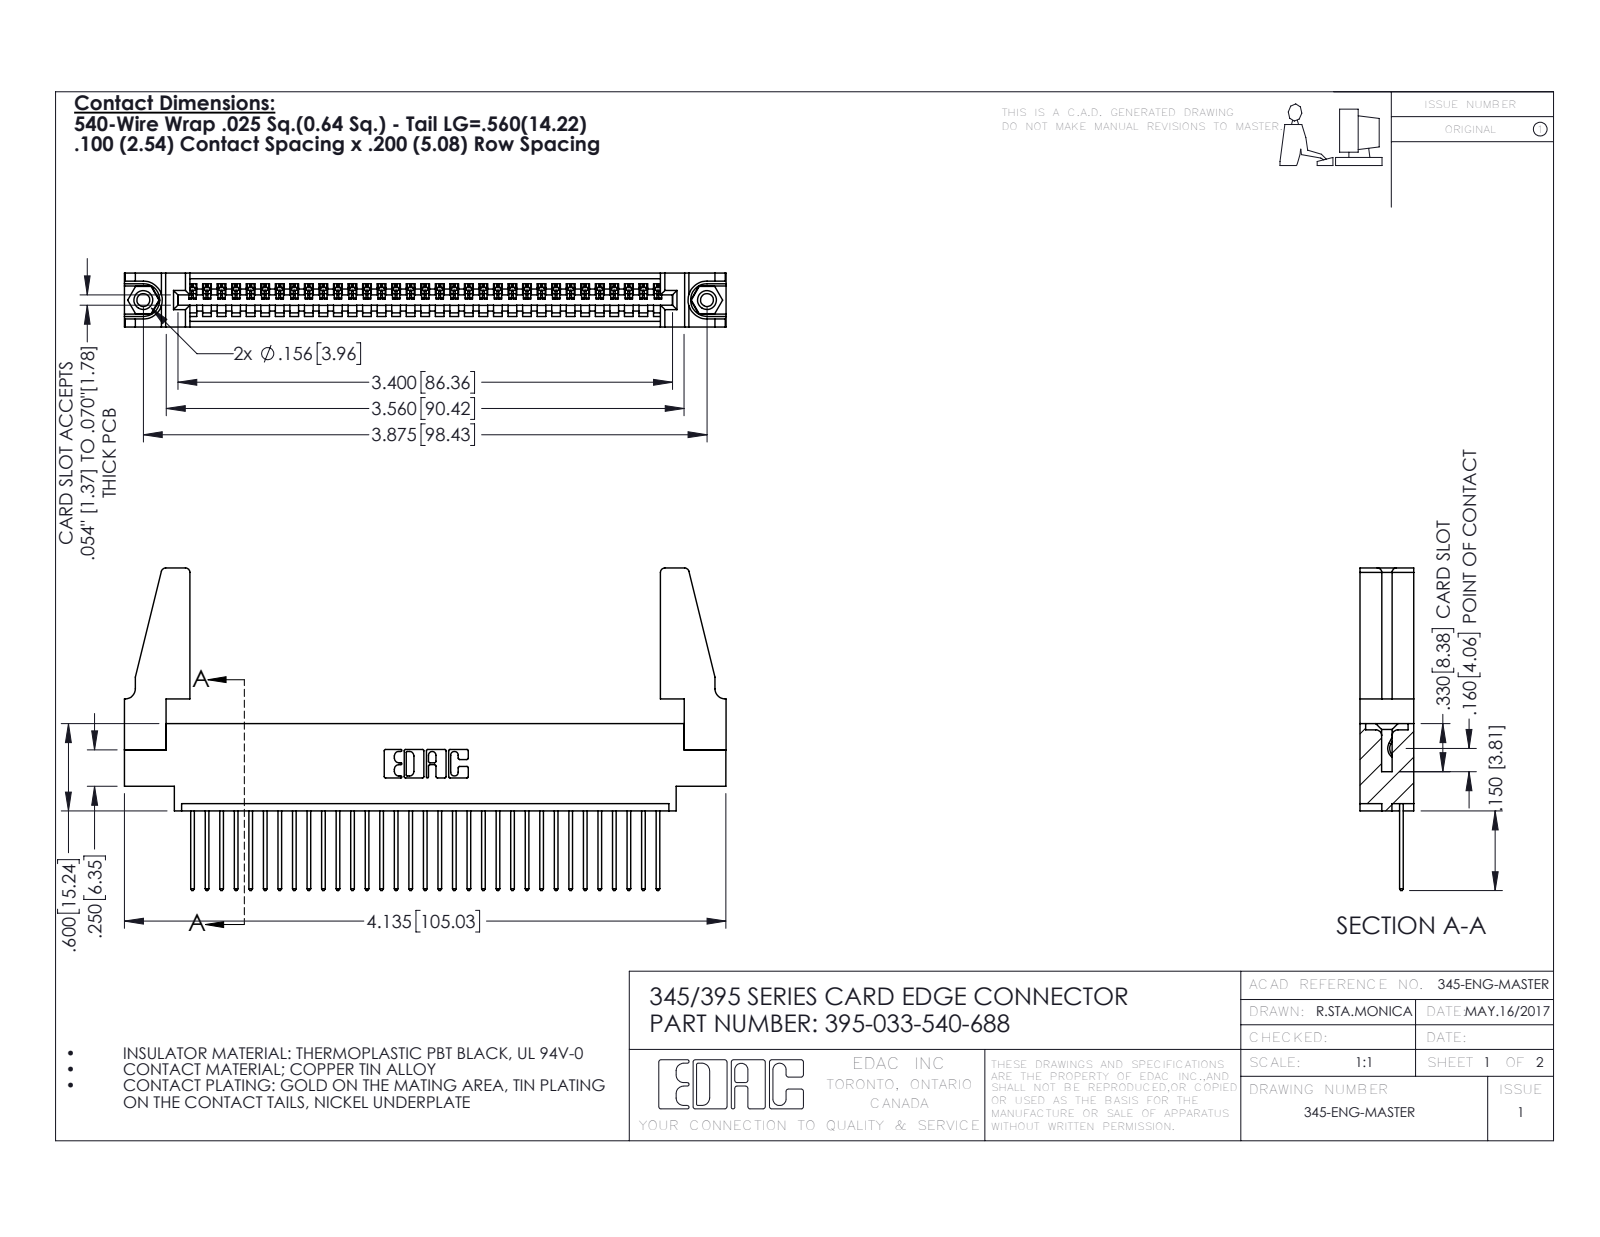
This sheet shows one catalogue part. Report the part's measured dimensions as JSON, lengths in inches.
{"part_name": "345-292-001_345-293-140; 345-220-078_345-220-088; 395-033-540-688; 345 Part_0.170 Offset - 0.156 Dia-TH (+1 more)", "step_written_by": "SolidWorks 2016 (CONFIG_CONTROL_DESIGN)", "units": "inches", "bodies": {"solids": 38, "faces": 2168, "planar": 1476, "cylindrical": 676, "other": 16}, "overall_size": [4.136, 2.217, 0.37], "volume_in3": 0.799, "surface_area_in2": 25.62, "round_holes": [[0.089, 2], [0.125, 2], [0.156, 2], [0.064, 1]], "round_bosses_or_shafts": [[0.155, 2]], "partial_cylinders_radius": [[0.006, 66], [0.01, 66], [0.01, 22], [0.03, 8], [0.007, 6], [0.031, 6], [0.026, 3], [0.031, 2]], "face_to_face_distances": [0.072, 0.37, 0.298, 0.098, 0.272, 0.025, 0.2, 0.225, 0.175, 0.149], "hole_center_spacings": [0.27, 3.64, 3.875]}
